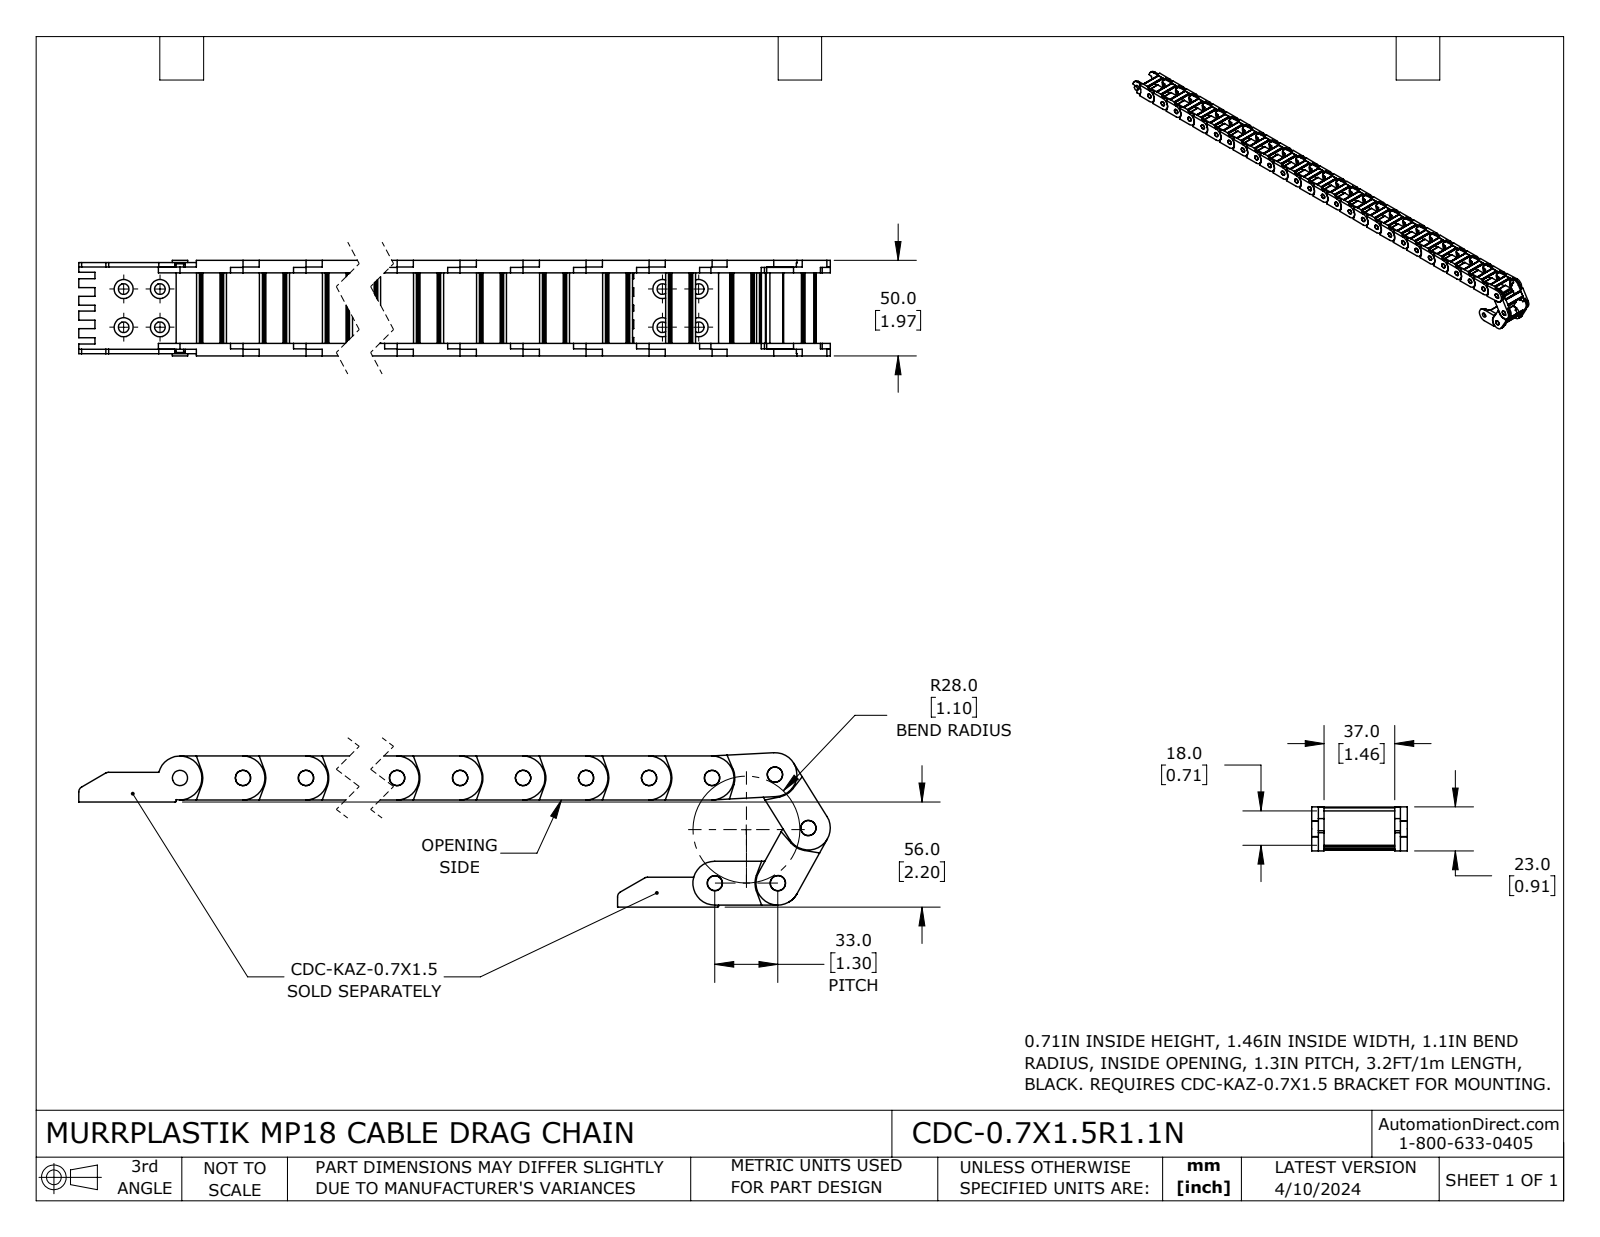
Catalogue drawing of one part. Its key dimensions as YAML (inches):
part_name: "CDC-0.7X1.5R1.1N"
step_written_by: "SolidWorks 2023 (CONFIG_CONTROL_DESIGN)"
units: inches
bodies: {solids: 30, faces: 2370, planar: 1110, cylindrical: 1260, other: 0}
overall_size: [36.665, 3.143, 1.969]
volume: 19.75
surface_area: 377.9
round_holes:
  - {diameter: 0.315, count: 30}
round_bosses_or_shafts:
  - {diameter: 0.315, count: 1}
partial_cylinders:
  - {radius: 0.02, count: 120}
  - {radius: 0.059, count: 120}
  - {radius: 0.008, count: 60}
  - {radius: 0.012, count: 60}
  - {radius: 0.453, count: 31}
  - {radius: 0.47, count: 31}
  - {radius: 0.197, count: 30}
  - {radius: 0.215, count: 30}
face_to_face_distances: [0.256, 1.713, 1.969, 0.138, 1.831, 0.118, 1.575, 0.146, 1.823, 1.685]
hole_center_spacings: [1.299, 2.598, 3.898, 5.197, 6.496, 7.795, 9.094, 10.394]
